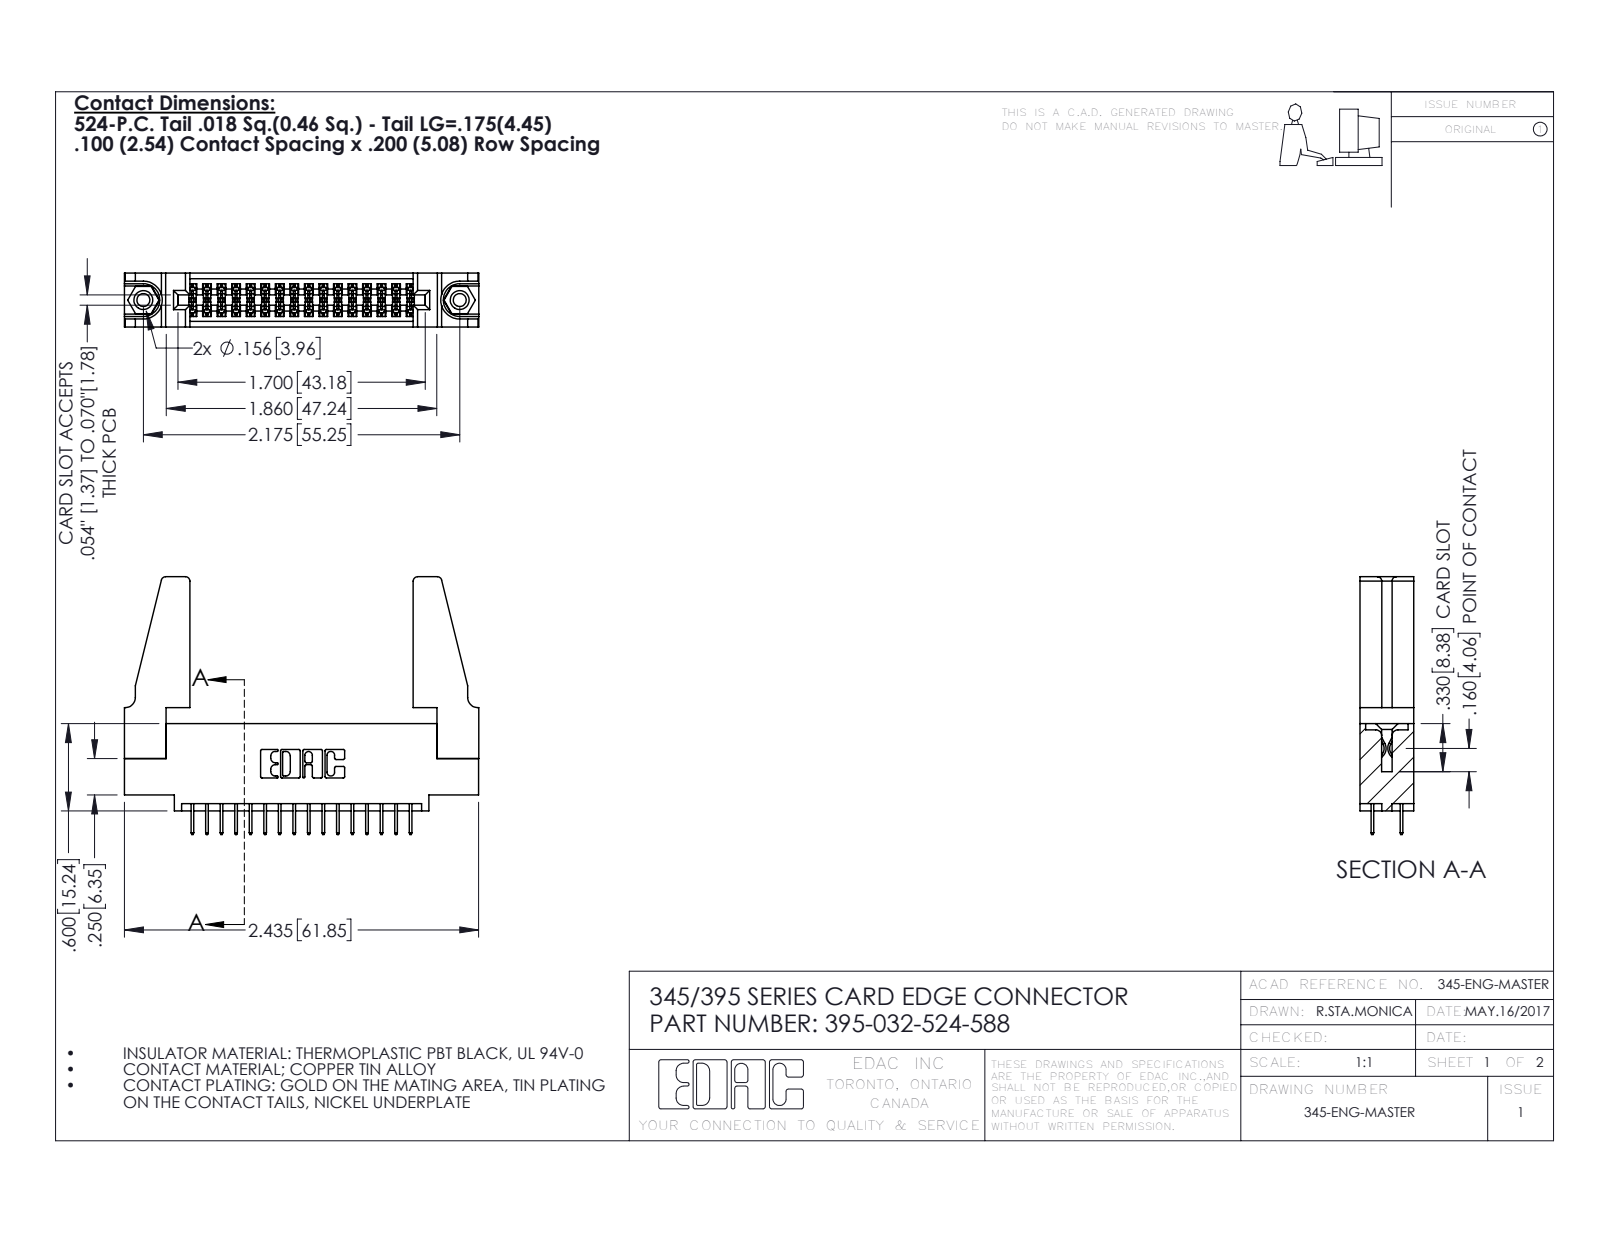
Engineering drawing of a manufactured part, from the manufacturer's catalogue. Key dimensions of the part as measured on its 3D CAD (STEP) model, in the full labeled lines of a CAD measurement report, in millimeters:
Part name (STEP PRODUCT): 345-292-001_345-293-124; 345-250-001_345-250-001-102; 345 Part_0.110 Offset - 0.156 Dia-TH; 395-032-524-588 (+1 more)
STEP written by: SolidWorks 2016 (CONFIG_CONTROL_DESIGN)
Units: millimetres
Bodies: 37 solids, 1982 faces (1404 planar, 562 cylindrical, 16 other)
Overall size (bounding box): 61.9 × 45 × 9.4
Volume: 8 900 mm³ · Surface area: 10 930 mm²
Round holes (diameter × count): ⌀2.3 ×2, ⌀3.2 ×2, ⌀4 ×2, ⌀1.6 ×1
Round bosses / shafts (diameter × count): ⌀3.9 ×2
Partial cylindrical surfaces — rounded edges, fillets, slot ends (radius × count): R0.2 ×48, R0.3 ×22, R0.8 ×8, R0.2 ×6, R0.8 ×6, R0.7 ×3, R0.4 ×2, R0.5 ×2
Main face-to-face distances: 9.4, 1.8, 7.6, 5.1, 2.5, 6.9, 0.6, 5.7, 1.8, 3.8
Hole centre spacings: 6.9, 49.3, 55.2
